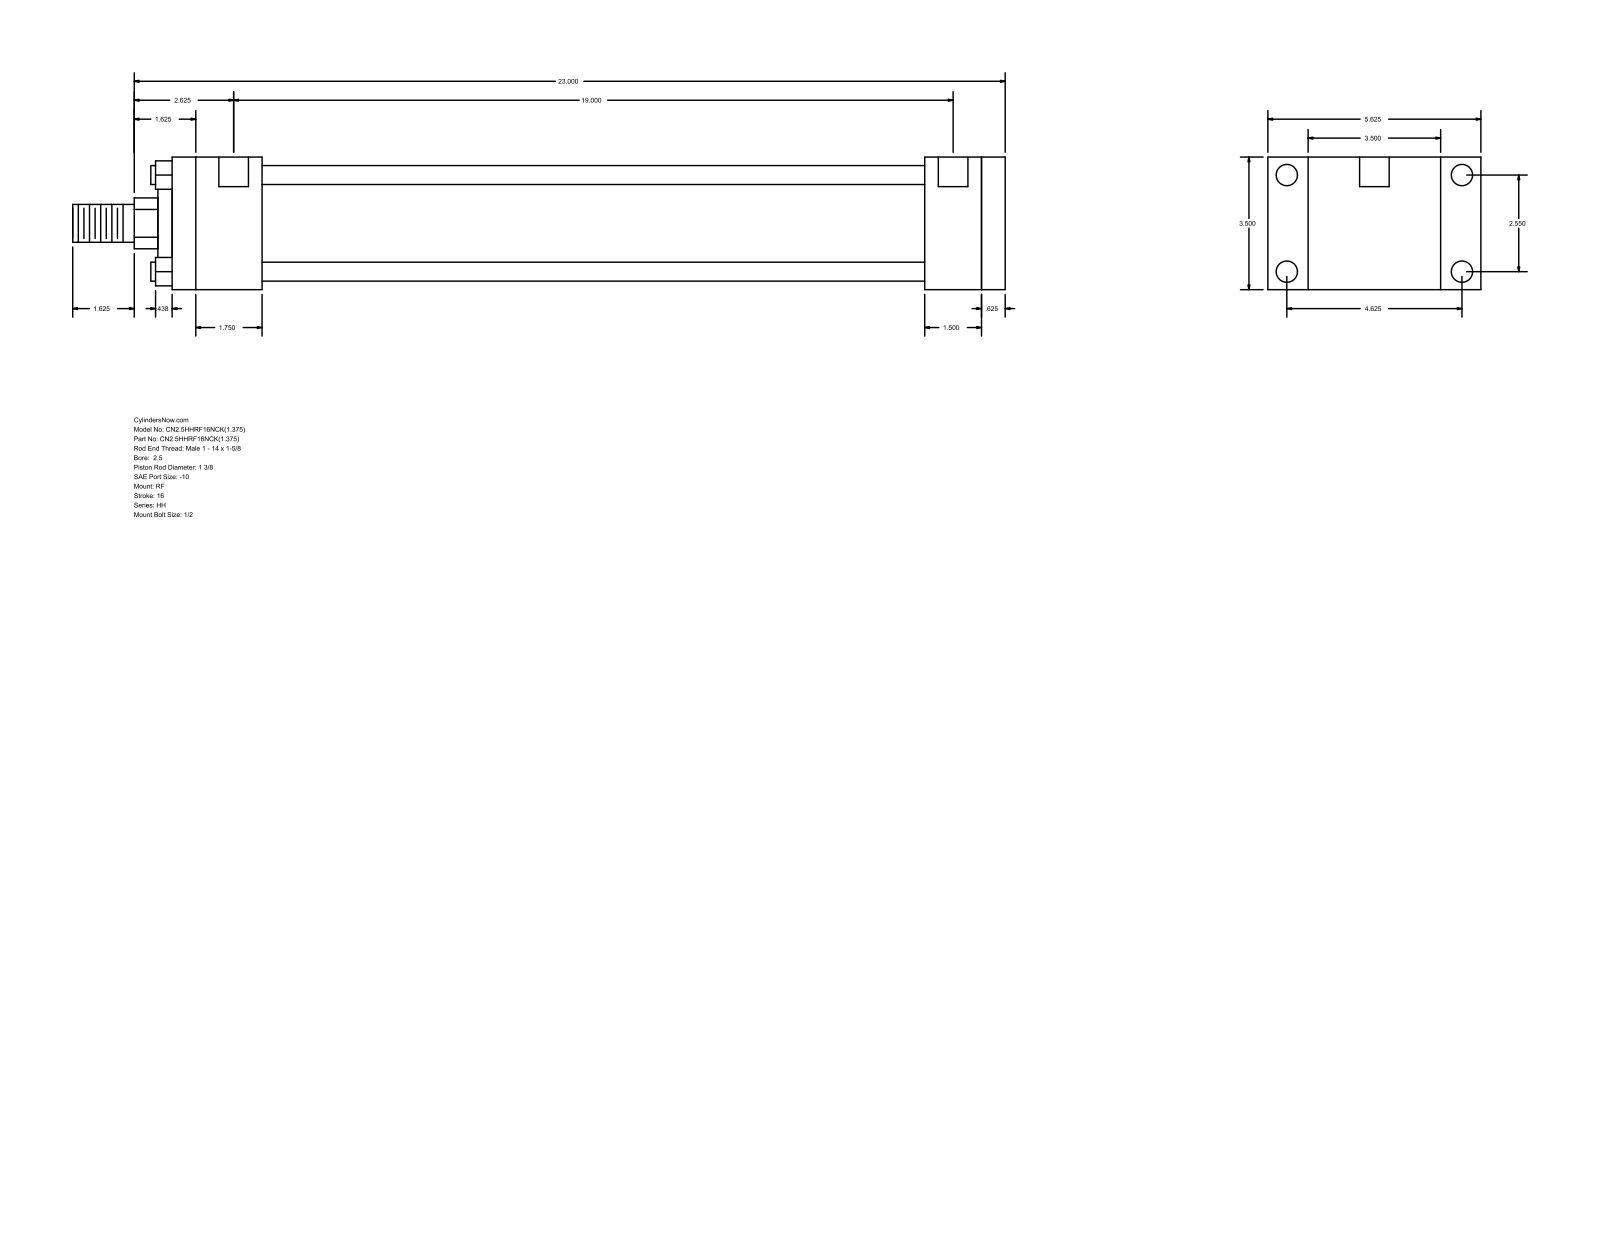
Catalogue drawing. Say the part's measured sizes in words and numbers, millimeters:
The part is named "HH_RF__0250_1.375". Its 3-D file was written by "GSSL Pune (CONFIG_CONTROL_DESIGN)". It is 0 solids with 92 faces: 64 planar, 28 cylindrical and 0 other. Overall it measures 625.48 by 142.88 by 88.9 millimeters. Round holes: 4 of diameter 5.56, 4 of diameter 14.3, 2 of diameter 19.84. Round bosses or shafts: 4 of diameter 12.7, 1 of diameter 73.03, 1 of diameter 50.8, 1 of diameter 34.92, 1 of diameter 25.4. Partial cylindrical surfaces (rounded edges, fillets, slot ends): 1 of radius 17.06. The main face-to-face distances are 88.9, 558.8, 542.93, 15.87, 53.97, 60.32, 482.61, 498.48, 504.83, 444.51. The hole center spacings are 64.76, 117.48, 134.15, 485.77, 1.58, 1.59, 482.6, 484.18.
